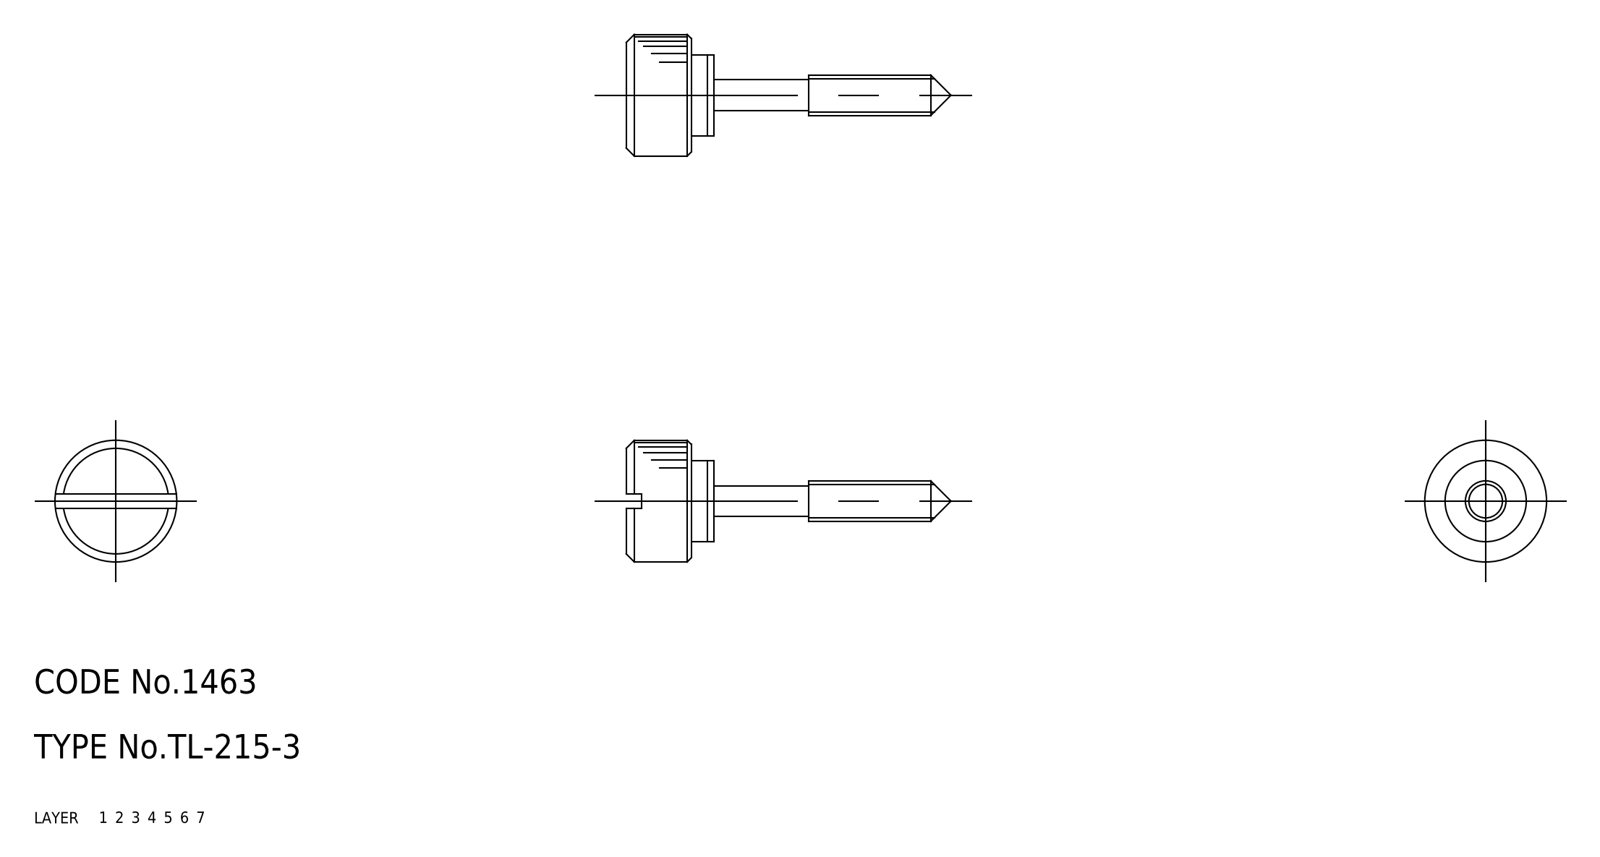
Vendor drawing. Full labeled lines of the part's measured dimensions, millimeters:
Part name (STEP PRODUCT): washer; knob; TL_215_3_25845_36
STEP written by: CADfix (AUTOMOTIVE_DESIGN)
Units: millimetres
Bodies: 2 solids, 42 faces (0 planar, 0 cylindrical, 42 other)
Overall size (bounding box): 40 × 15 × 15
Volume: 1 998 mm³ · Surface area: 1 372 mm²
